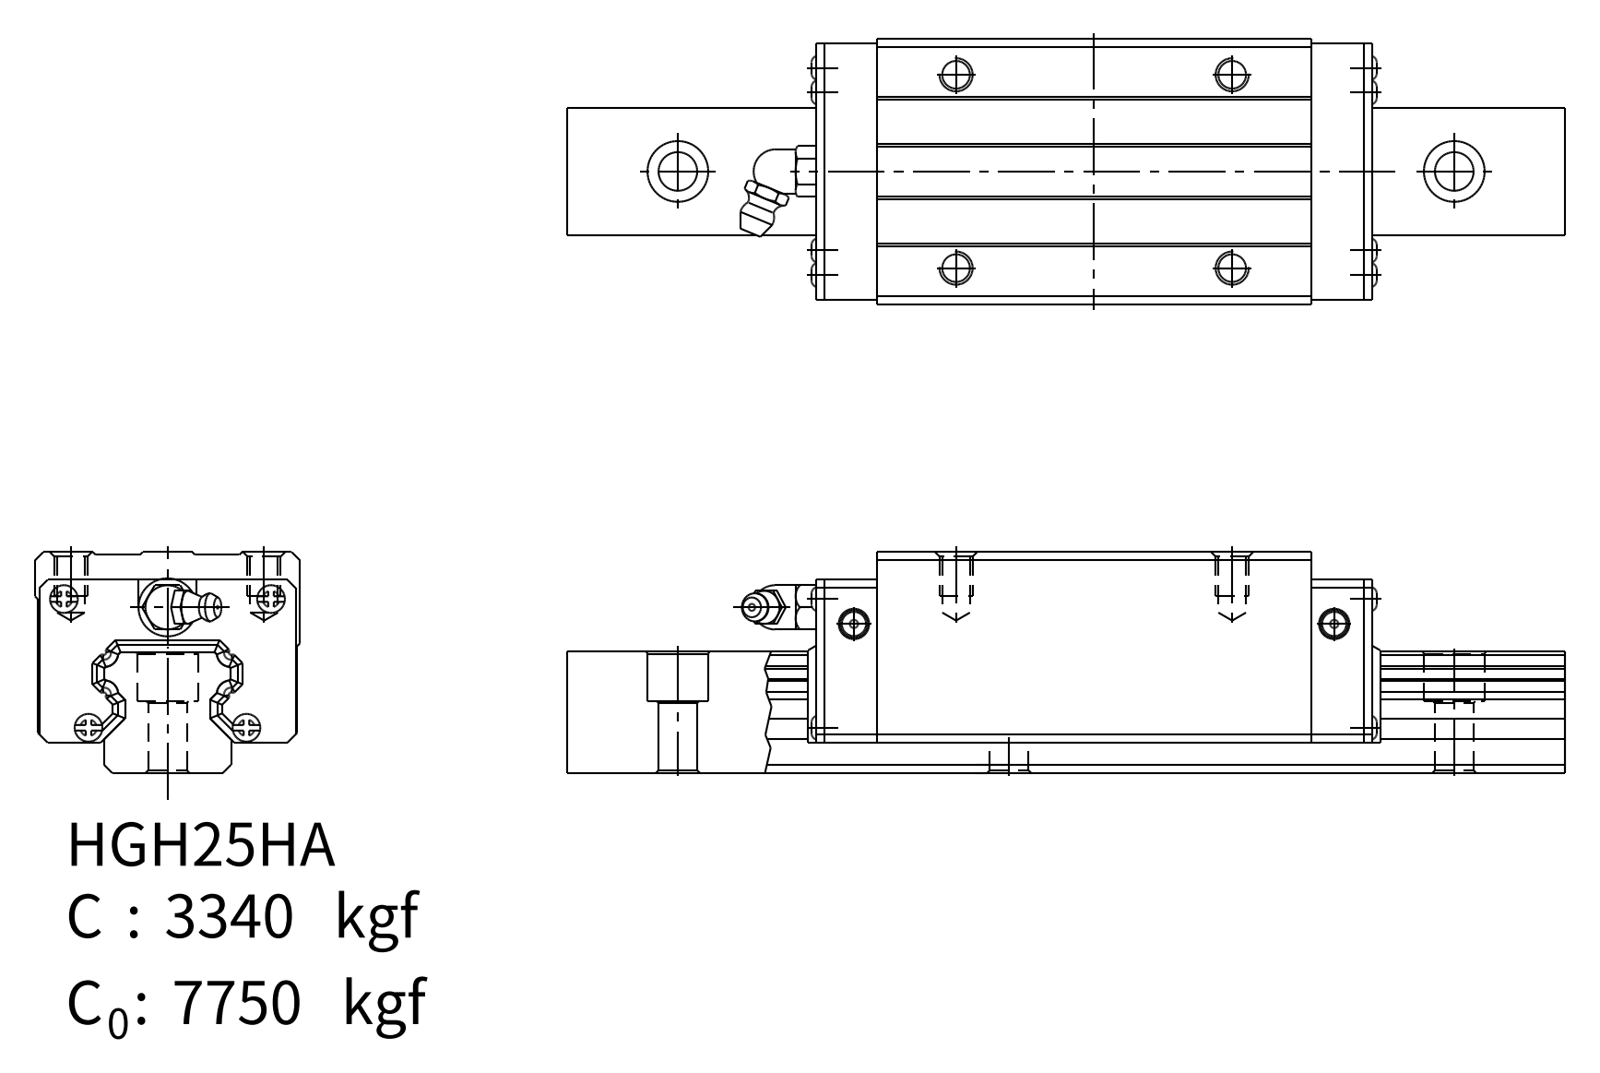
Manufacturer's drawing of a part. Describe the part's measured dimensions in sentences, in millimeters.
The part is named "HGH25HA". Its 3-D file was written by "SolidWorks 2006104 (CONFIG_CONTROL_DESIGN)". It is 1 solid with 360 faces: 270 planar, 30 cylindrical and 60 other. Overall it measures 104.9 by 48 by 34.5 millimeters. Its volume is 130 494 cubic millimeters and its surface area 23 643 square millimeters. Round holes: 4 of diameter 6. Partial cylindrical surfaces (rounded edges, fillets, slot ends): 12 of radius 0.5, 6 of radius 1, 4 of radius 2.43. The main face-to-face distances are 34.5, 47.7, 16.5, 18, 0.5, 34, 17.5, 104.6, 29.53, 13.03. The hole center spacings are 35, 50, 61.03.
